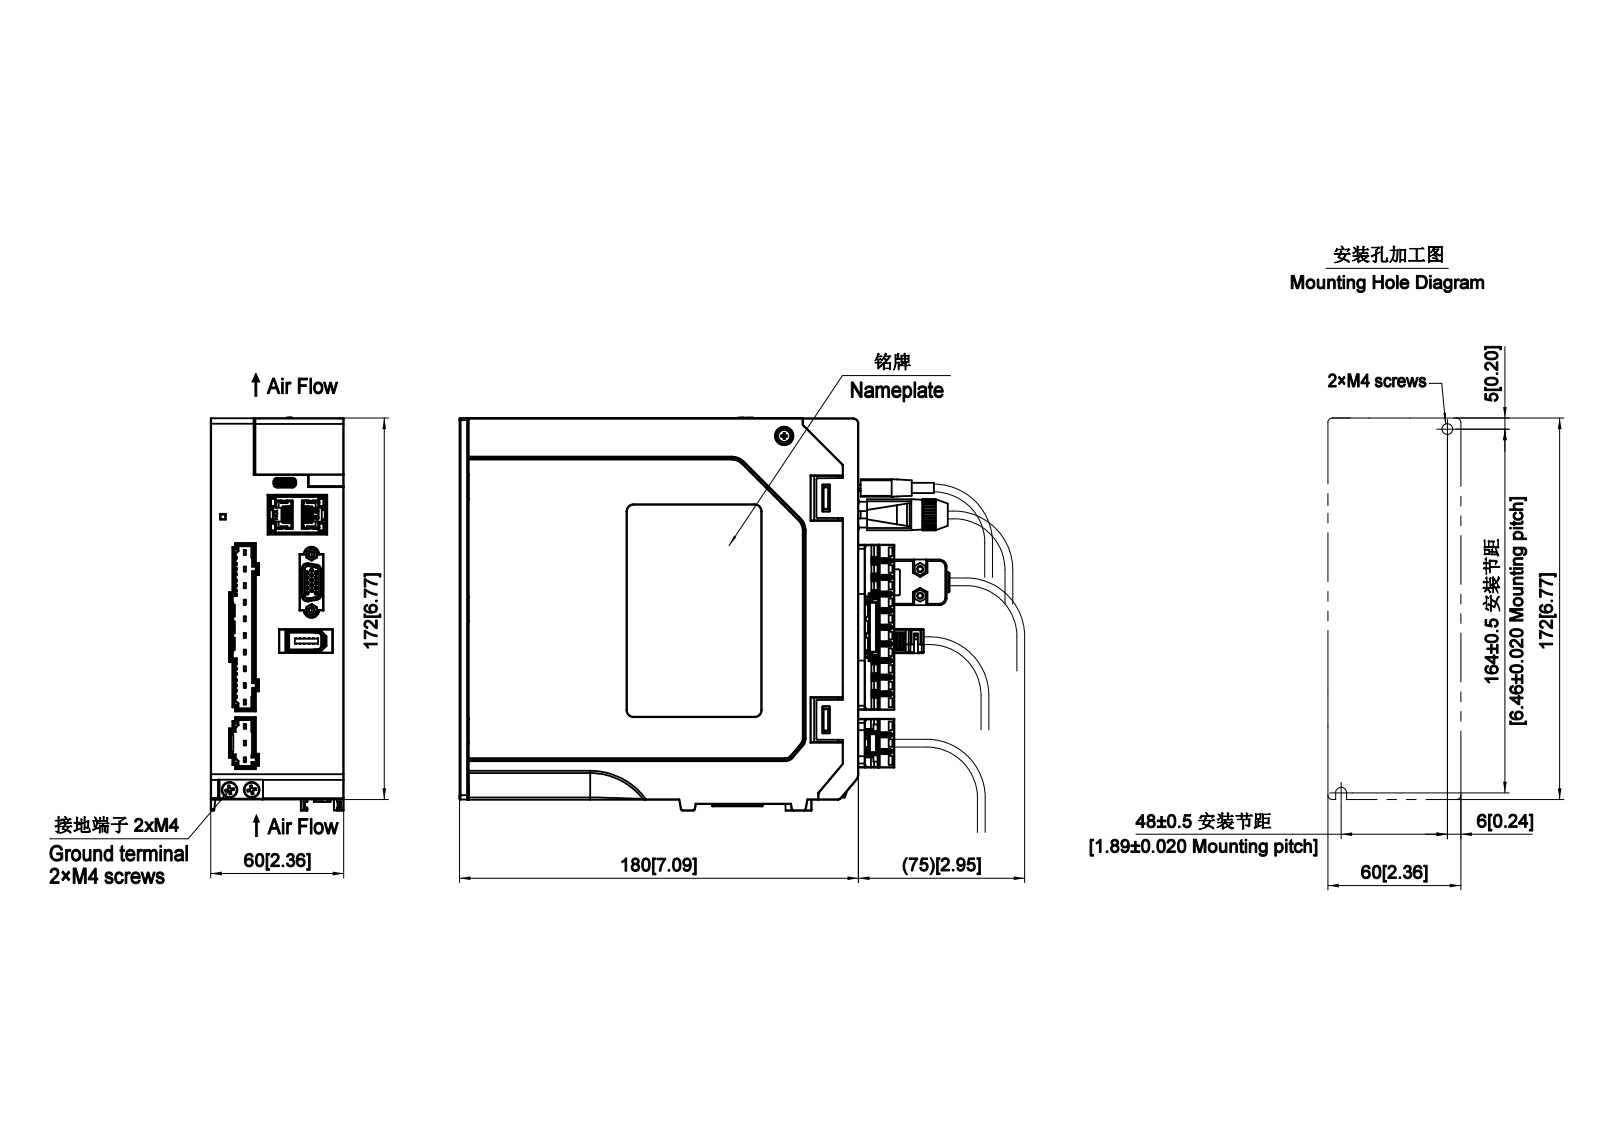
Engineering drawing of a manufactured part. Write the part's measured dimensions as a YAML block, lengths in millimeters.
part_name: "实体1"
step_written_by: "Spatial InterOp 3D (AUTOMOTIVE_DESIGN)"
units: millimeters
bodies: {solids: 96, faces: 16624, planar: 9091, cylindrical: 4970, other: 2563}
overall_size: [183, 177.3, 60]
round_holes:
  - {diameter: 2.5, count: 16}
  - {diameter: 0.9, count: 15}
  - {diameter: 3.5, count: 10}
  - {diameter: 0.67, count: 4}
  - {diameter: 1.25, count: 4}
  - {diameter: 3.3, count: 4}
  - {diameter: 4, count: 4}
  - {diameter: 2.2, count: 3}
  - {diameter: 4.4, count: 3}
  - {diameter: 4.5, count: 3}
  - {diameter: 5, count: 3}
  - {diameter: 2.26, count: 2}
round_bosses_or_shafts:
  - {diameter: 1, count: 16}
  - {diameter: 0.5, count: 12}
  - {diameter: 3, count: 5}
  - {diameter: 2.3, count: 4}
  - {diameter: 7.27, count: 3}
  - {diameter: 6.8, count: 3}
  - {diameter: 6.73, count: 3}
  - {diameter: 4, count: 3}
partial_cylinders:
  - {radius: 0.8, count: 759}
  - {radius: 0.2, count: 606}
  - {radius: 0.5, count: 485}
  - {radius: 0.3, count: 364}
  - {radius: 0.15, count: 289}
  - {radius: 0.1, count: 150}
  - {radius: 0.25, count: 121}
  - {radius: 1, count: 89}
face_to_face_distances: [2.2, 57.8, 5, 9, 2, 10, 6.8, 51, 6, 7]
hole_center_spacings: [2.29, 3.96, 6.05, 2.28, 4.58, 4.57, 3.97, 6.87]
